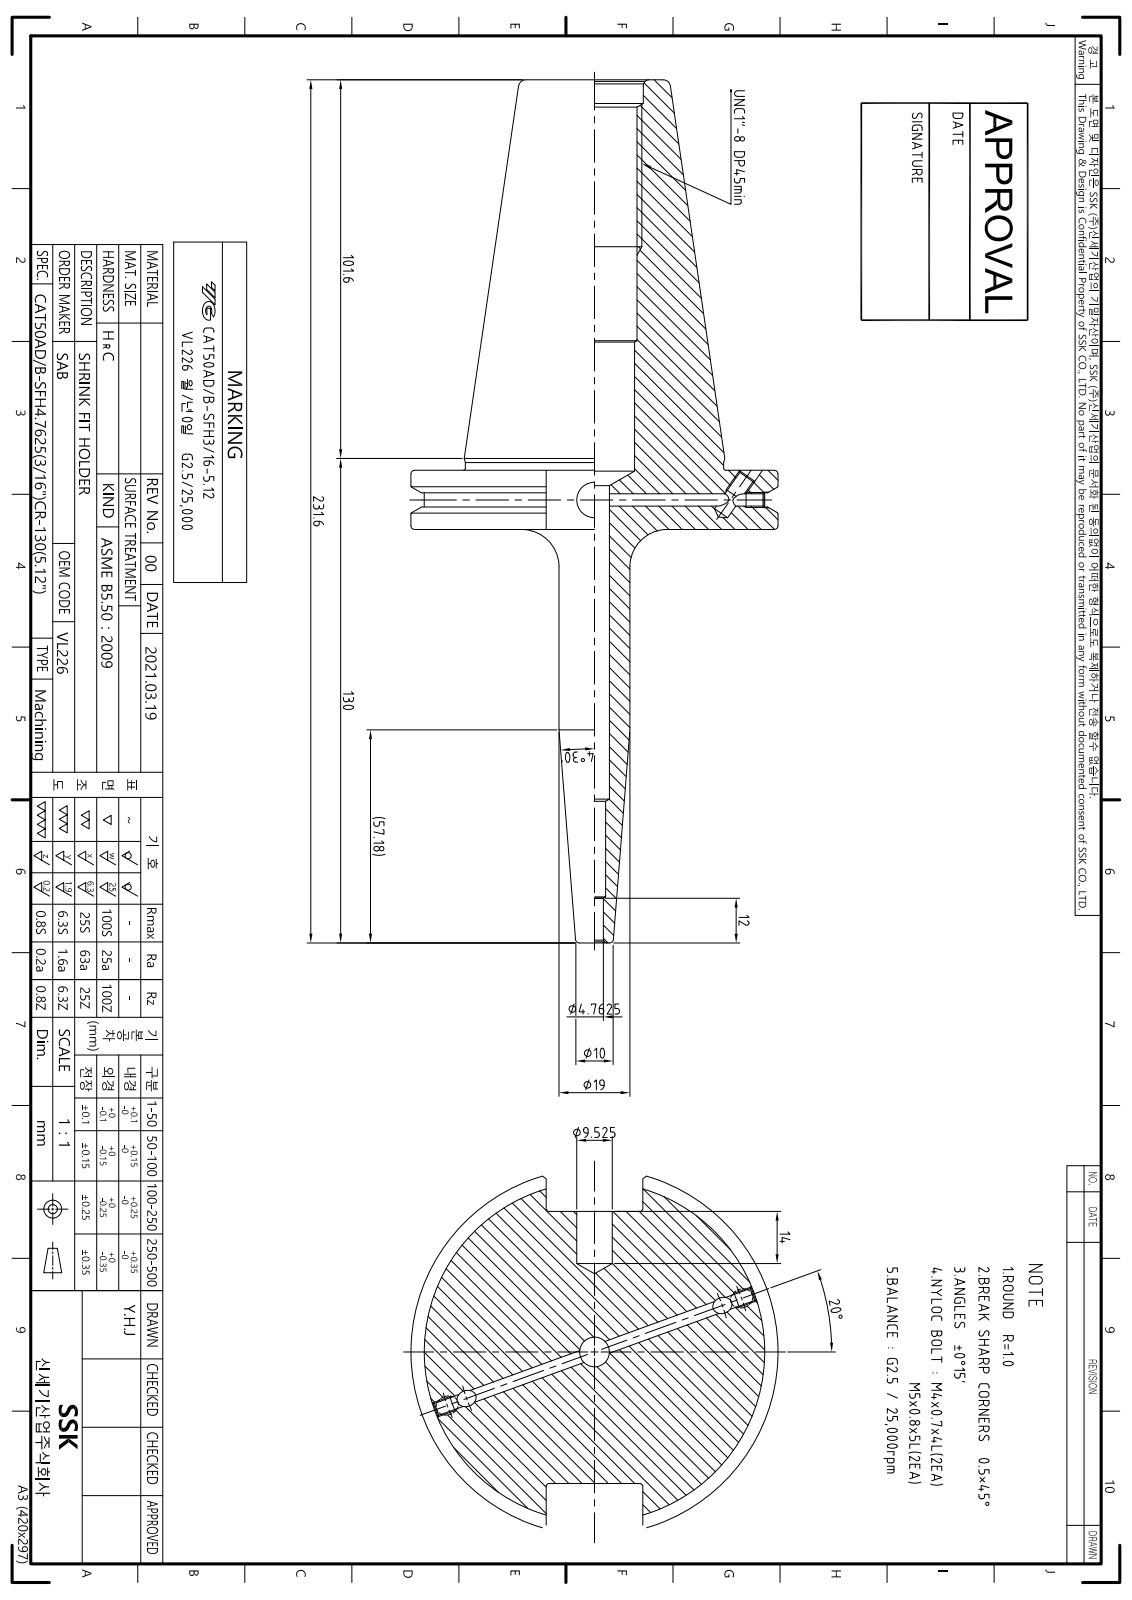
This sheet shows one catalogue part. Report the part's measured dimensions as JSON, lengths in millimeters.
{"part_name": "CAT50ADB-SFH4.7625-130", "step_written_by": "Autodesk Inventor 2022 (AUTOMOTIVE_DESIGN)", "units": "millimeters", "bodies": {"solids": 1, "faces": 85, "planar": 35, "cylindrical": 27, "other": 23}, "overall_size": [231.6, 98.42, 94.69], "volume_mm3": 344879, "surface_area_mm2": 52627, "round_holes": [[3.24, 2], [4.13, 2], [4.2, 2], [5, 2], [4.76, 1], [6, 1], [8, 1], [9.53, 1], [21.5, 1], [21.97, 1], [26.2, 1]], "round_bosses_or_shafts": [[98.42, 1], [91.29, 1], [69.25, 1], [19, 1]], "face_to_face_distances": [15.88, 104.77, 120.65, 73.03, 25.9, 110.82, 6.05, 9.83, 114.65, 9.88]}
